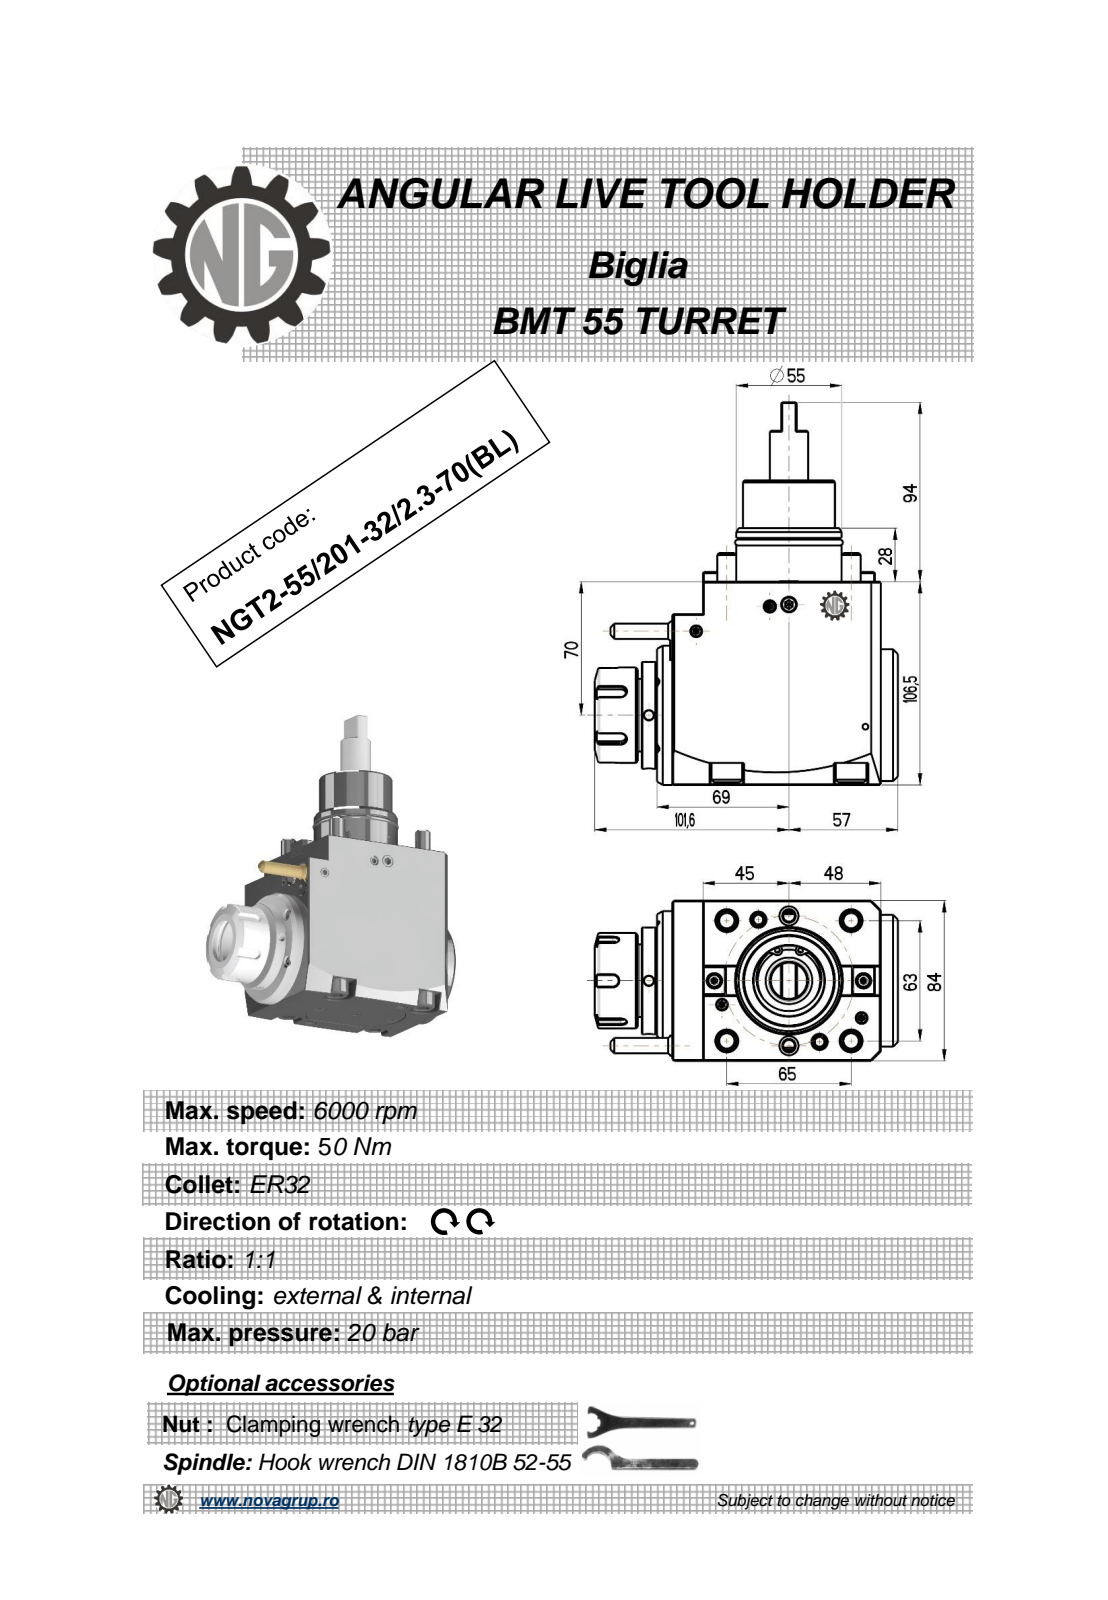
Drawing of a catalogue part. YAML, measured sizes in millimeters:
part_name: "NGT2_55_201_32_1_3_70_BL"
step_written_by: "PRO/ENGINEER BY PARAMETRIC TECHNOLOGY CORPORATION, 2010280 (CONFIG_CONTROL_DESIGN)"
units: millimeters
bodies: {solids: 2, faces: 448, planar: 204, cylindrical: 114, other: 130}
overall_size: [200.5, 158.6, 85.6]
volume: 1196000
surface_area: 90791
round_holes:
  - {diameter: 5, count: 3}
  - {diameter: 6, count: 2}
  - {diameter: 3, count: 1}
  - {diameter: 27, count: 1}
round_bosses_or_shafts:
  - {diameter: 16, count: 4}
  - {diameter: 10, count: 4}
  - {diameter: 50, count: 2}
  - {diameter: 73, count: 1}
  - {diameter: 69, count: 1}
  - {diameter: 56, count: 1}
  - {diameter: 55, count: 1}
  - {diameter: 48, count: 1}
partial_cylinders:
  - {radius: 0.32, count: 20}
  - {radius: 0.22, count: 6}
  - {radius: 3, count: 5}
  - {radius: 8.5, count: 4}
  - {radius: 0.8, count: 2}
  - {radius: 480, count: 2}
  - {radius: 3.4, count: 1}
  - {radius: 4, count: 1}
face_to_face_distances: [84, 106.5, 9, 8, 118, 109, 16, 117, 126, 53]
hole_center_spacings: [80.76, 55.61, 68]
